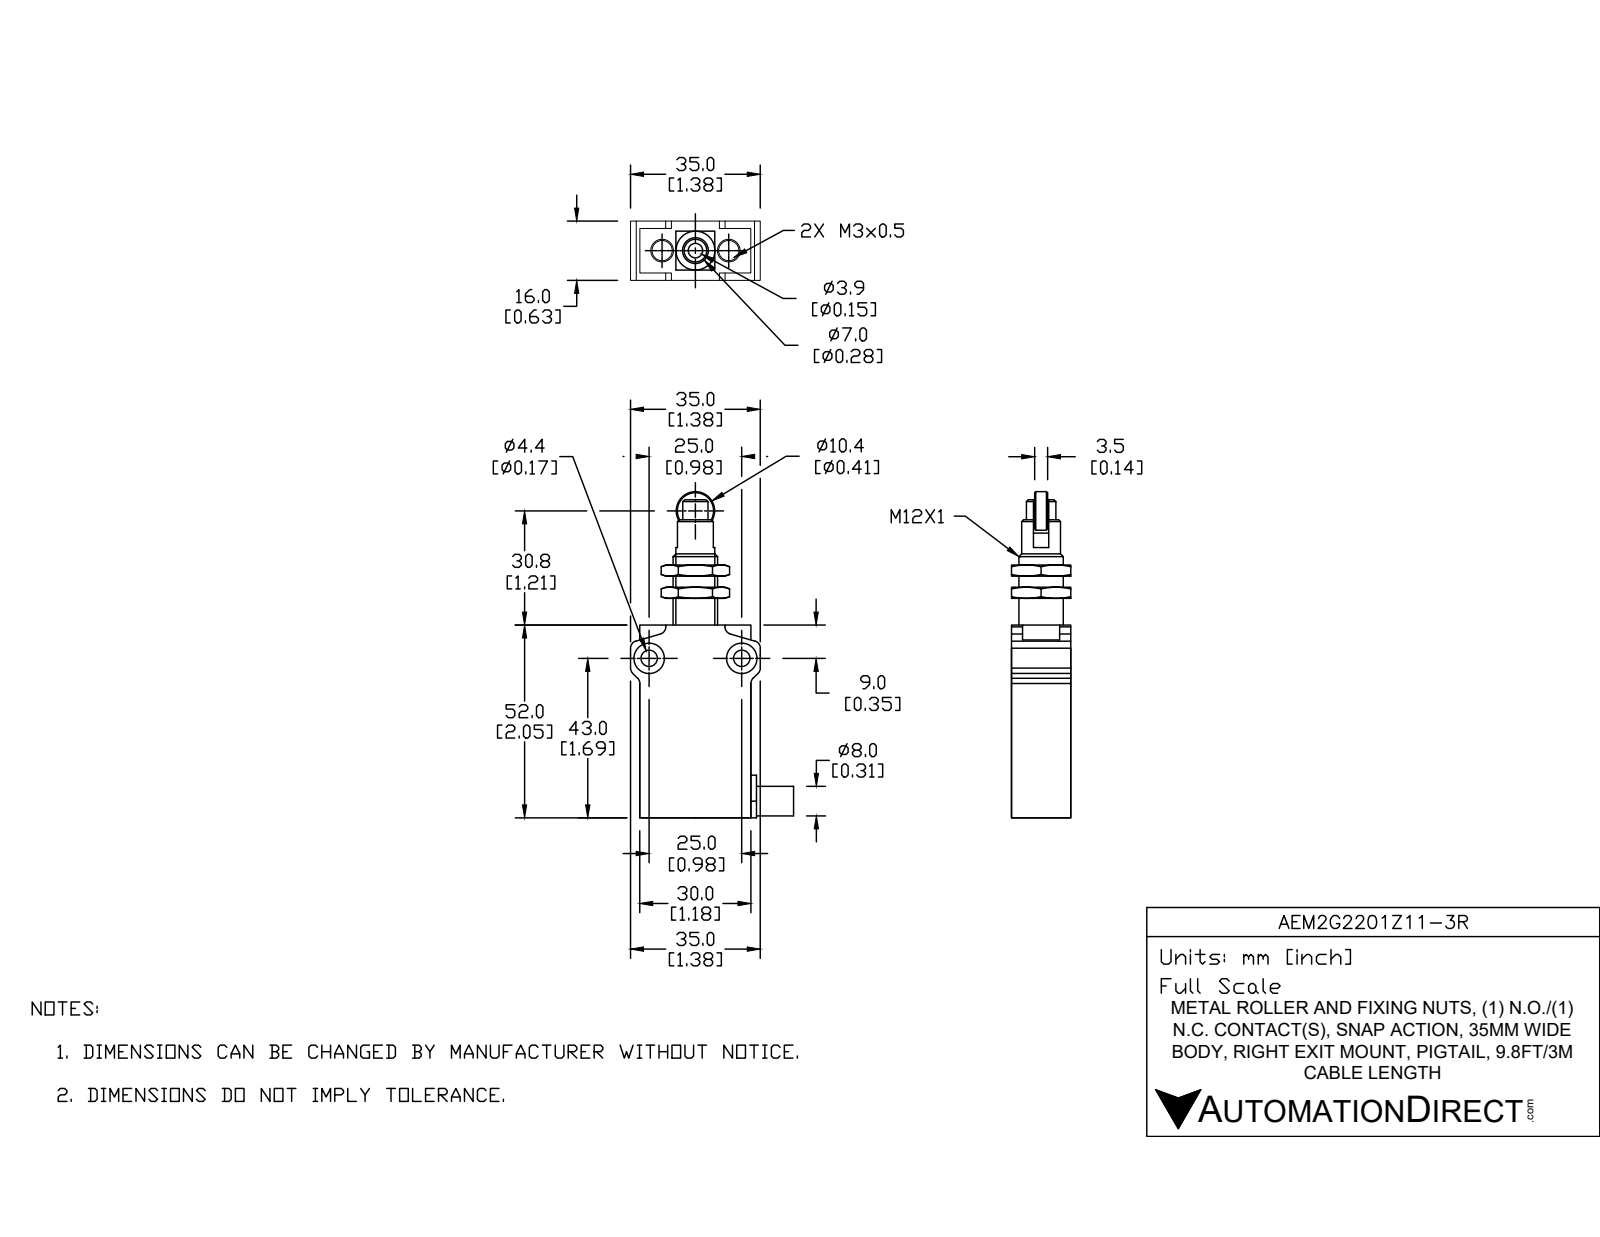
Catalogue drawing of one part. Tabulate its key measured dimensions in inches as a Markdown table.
| quantity | value |
| --- | --- |
| part name | AEM2G2201Z11-3R |
| STEP written by | SolidWorks 2017 (AUTOMOTIVE_DESIGN) |
| units | inches |
| bodies | 7 solids, 178 faces (79 planar, 56 cylindrical, 43 other) |
| overall size | 3.346 × 1.87 × 0.63 |
| volume | 1.658 in³ |
| surface area | 17.53 in² |
| round holes (diameter × count) | 0.118 × 2, 0.173 × 2, 0.323 × 2, 0.317 × 1, 0.472 × 1 |
| round bosses / shafts (diameter × count) | 0.413 × 1, 0.409 × 1, 0.323 × 1, 0.313 × 1, 0.22 × 1 |
| partial cylindrical surfaces (radius × count) | 0.079 × 8, 0.256 × 1 |
| main face-to-face distances | 0.63, 1.181, 0.472, 0.118, 0.236, 1.929, 1.74, 0.189, 0.354, 0.157 |
| hole center spacings | 0.374, 0.748, 0.984 |
